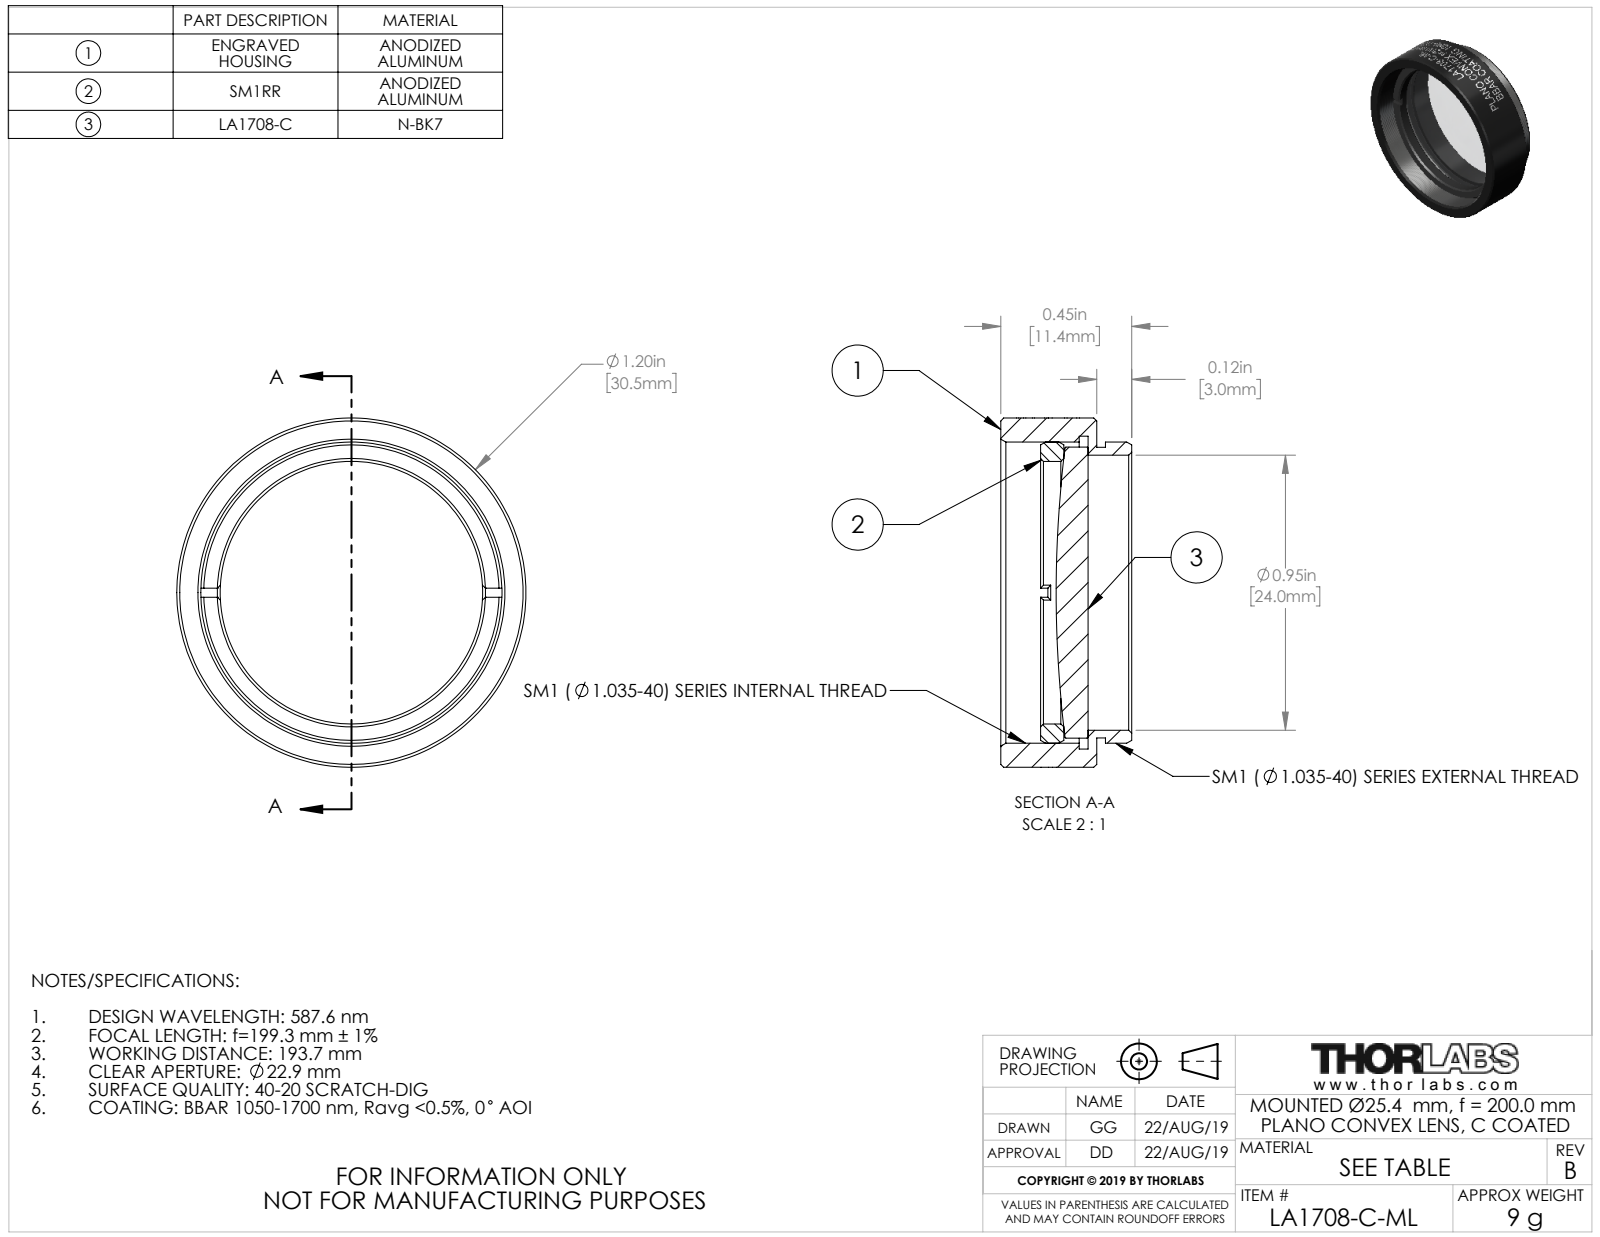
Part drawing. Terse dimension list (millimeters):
name: 24441-E0W
written by: SolidWorks 2018 (CONFIG_CONTROL_DESIGN)
unit: mm
bodies: 3 solids, 160 faces (20 planar, 112 cylindrical, 28 other)
size: 30.48 × 30.48 × 11.43
volume: 3 291 mm³; area: 4 308 mm²
holes: 1× ⌀22.91, 1× ⌀24, 1× ⌀26.29, 1× ⌀27.3
bosses: 1× ⌀30.48, 1× ⌀26.29, 1× ⌀25.4, 1× ⌀25.37
face distances: 0.76, 8.38, 7.62, 2.87, 2.11, 5.51, 4.9, 4.14, 2.03, 3.48
